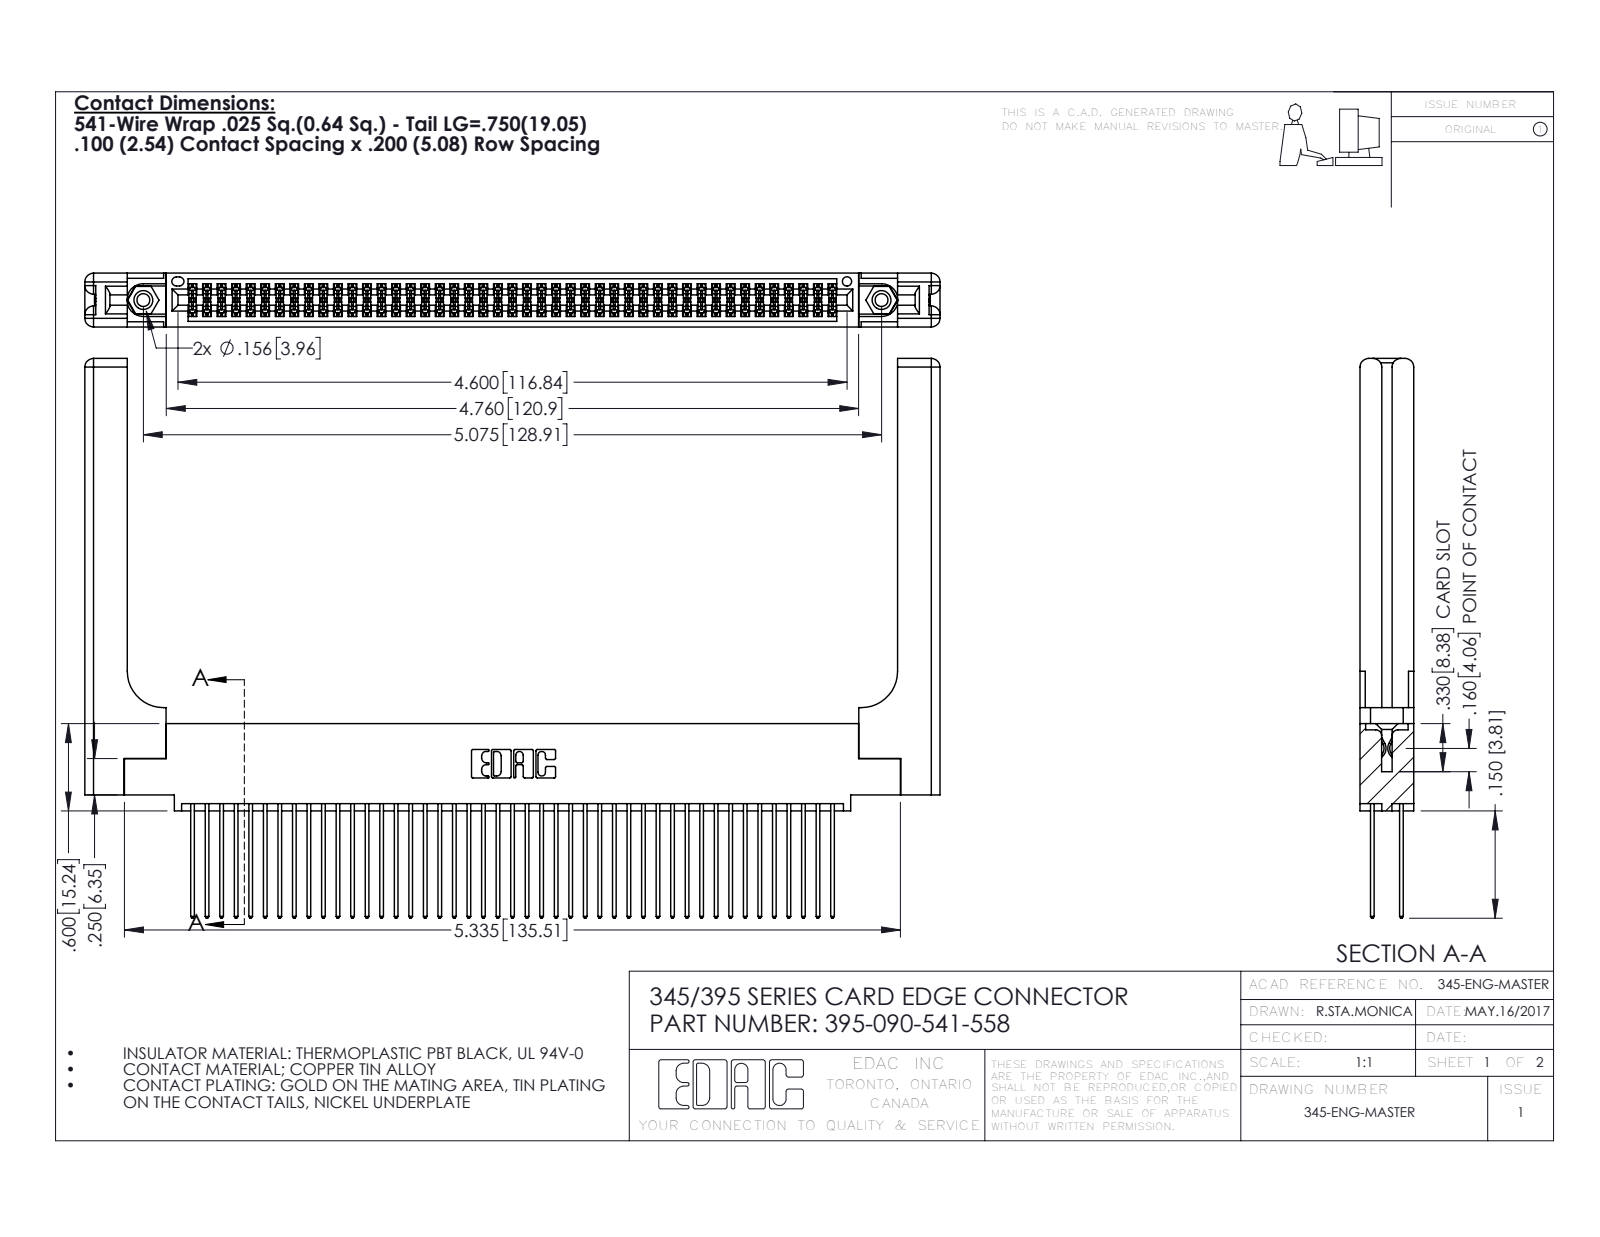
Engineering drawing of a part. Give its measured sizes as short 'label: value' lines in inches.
name: 345 Part_0.110 Offset - 0.156 Dia-TH; 345-292-001_345-293-141; 345-220-058_345-220-058; 345-250-001_345-250-001-102 (+1 more)
written by: SolidWorks 2016 (CONFIG_CONTROL_DESIGN)
unit: in
bodies: 95 solids, 4886 faces (3202 planar, 1624 cylindrical, 60 other)
size: 5.879 × 3.847 × 0.37
volume: 1.431 in³; area: 46.15 in²
holes: 2× ⌀0.089, 2× ⌀0.125, 2× ⌀0.156, 1× ⌀0.064
bosses: 2× ⌀0.155
rounds: 135× R0.006, 90× R0.01, 22× R0.01, 16× R0.06, 6× R0.007, 6× R0.031, 3× R0.026, 2× R0.014
face distances: 0.072, 0.298, 0.37, 0.098, 0.272, 0.025, 0.2, 0.225, 0.175, 0.148
hole spacings: 0.27, 4.839, 5.075
